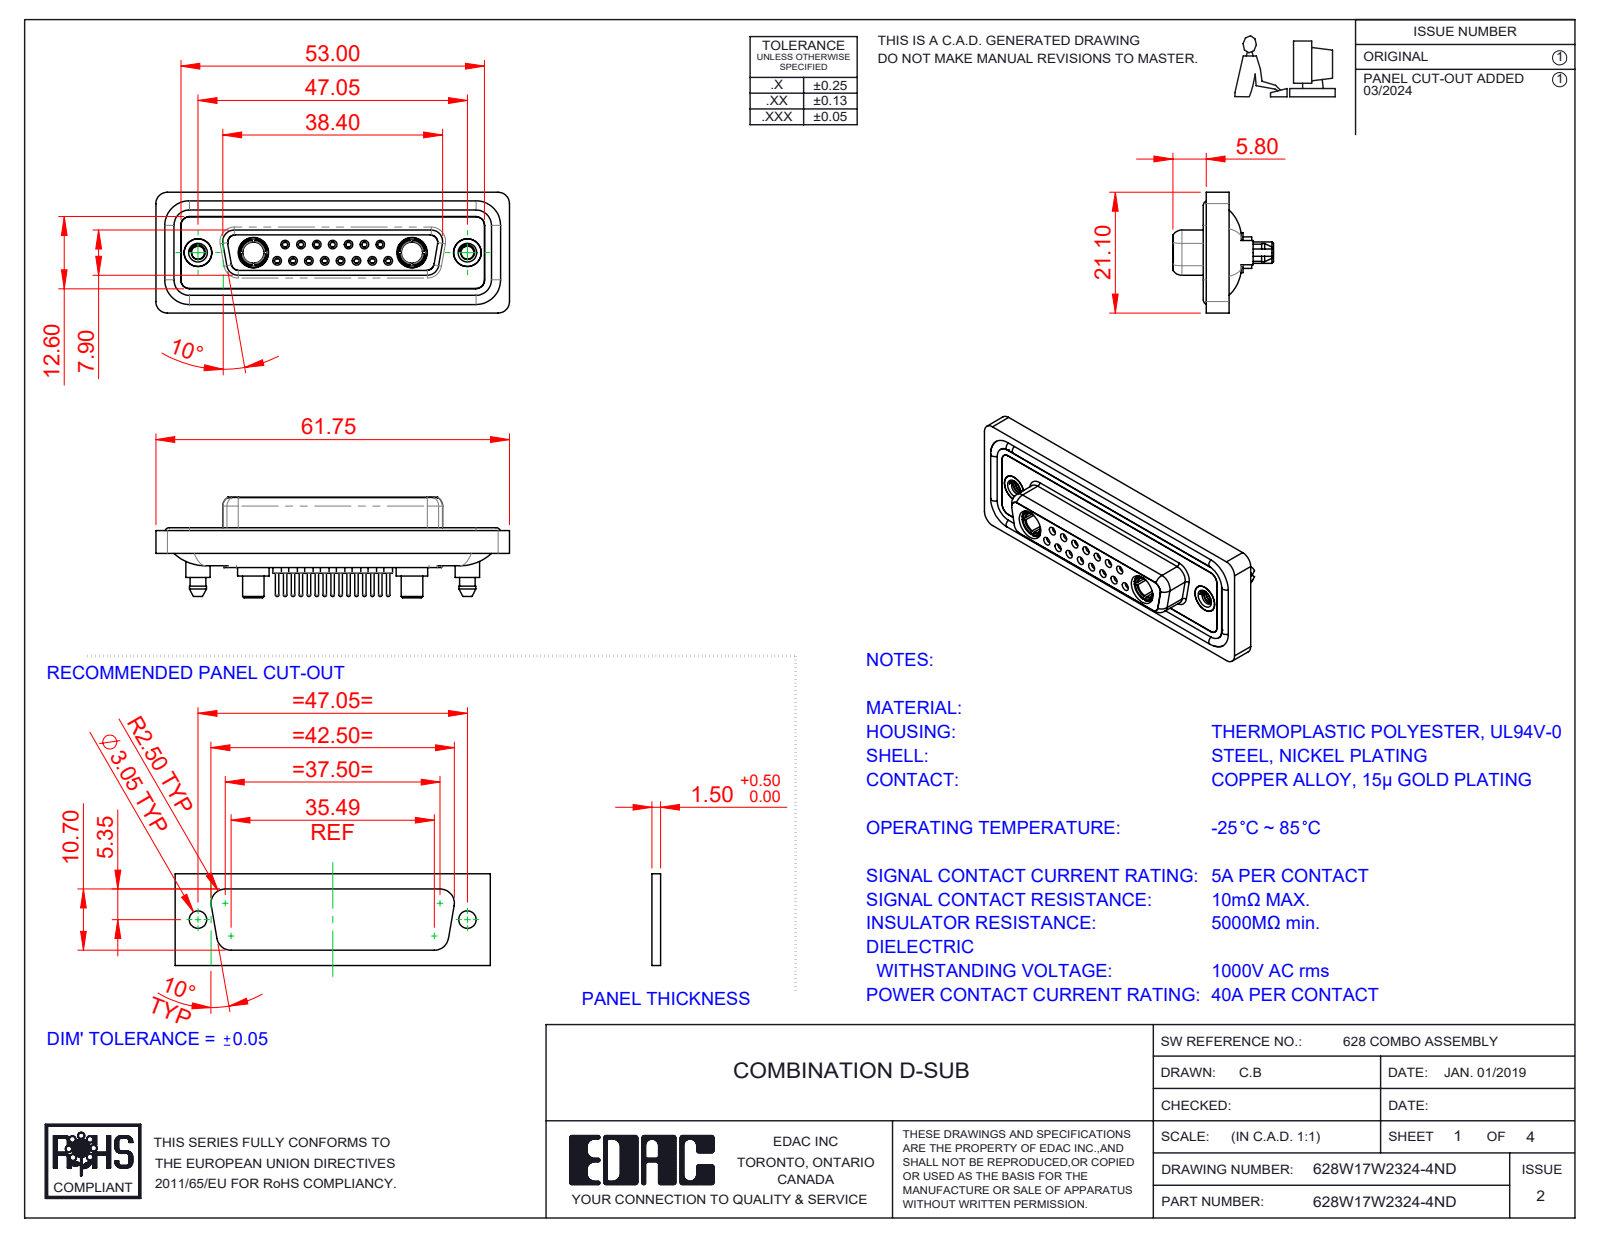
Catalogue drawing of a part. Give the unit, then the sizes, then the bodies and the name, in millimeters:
Units: millimetres
Overall size (bounding box): 61.75 × 21.1 × 17.55
Round holes (diameter × count): ⌀0.9 ×15, ⌀1.1 ×15, ⌀1.5 ×15, ⌀2 ×15, ⌀1.6 ×8, ⌀1.7 ×7, ⌀4.85 ×4, ⌀2.26 ×2, ⌀3.7 ×2, ⌀4 ×2, ⌀4.05 ×2, ⌀5 ×2
Round bosses / shafts (diameter × count): ⌀2.2 ×15, ⌀0.6 ×15, ⌀1.6 ×11, ⌀5.5 ×2, ⌀5.4 ×2, ⌀5.2 ×2, ⌀4.96 ×2, ⌀4.95 ×2
Partial cylindrical surfaces — rounded edges, fillets, slot ends (radius × count): R1.5 ×24, R2 ×18, R1.6 ×10, R1.35 ×8, R0.25 ×4, R0.5 ×4, R0.6 ×4, R0.65 ×4
Main face-to-face distances: 0.4, 1.8, 7.45, 5.65, 6.6, 0.5, 7.05, 1.6, 2.9, 1.1
Hole centre spacings: 3.16, 2.77, 8.31, 5.54, 5.03, 5.04, 7.49, 11.08
Volume: 8 496 mm³ · Surface area: 14 216 mm²
Bodies: 26 solids, 1425 faces (404 planar, 567 cylindrical, 454 other)
Part name (STEP PRODUCT): 628Combo Shell Rear_25 Contacts; 628Combo Threaded Boardlock_D; 628Combo Shell Front_25 Contacts; 628Combo Contact Row 2_24 (+5 more)
STEP written by: SolidWorks 2023 (CONFIG_CONTROL_DESIGN)
